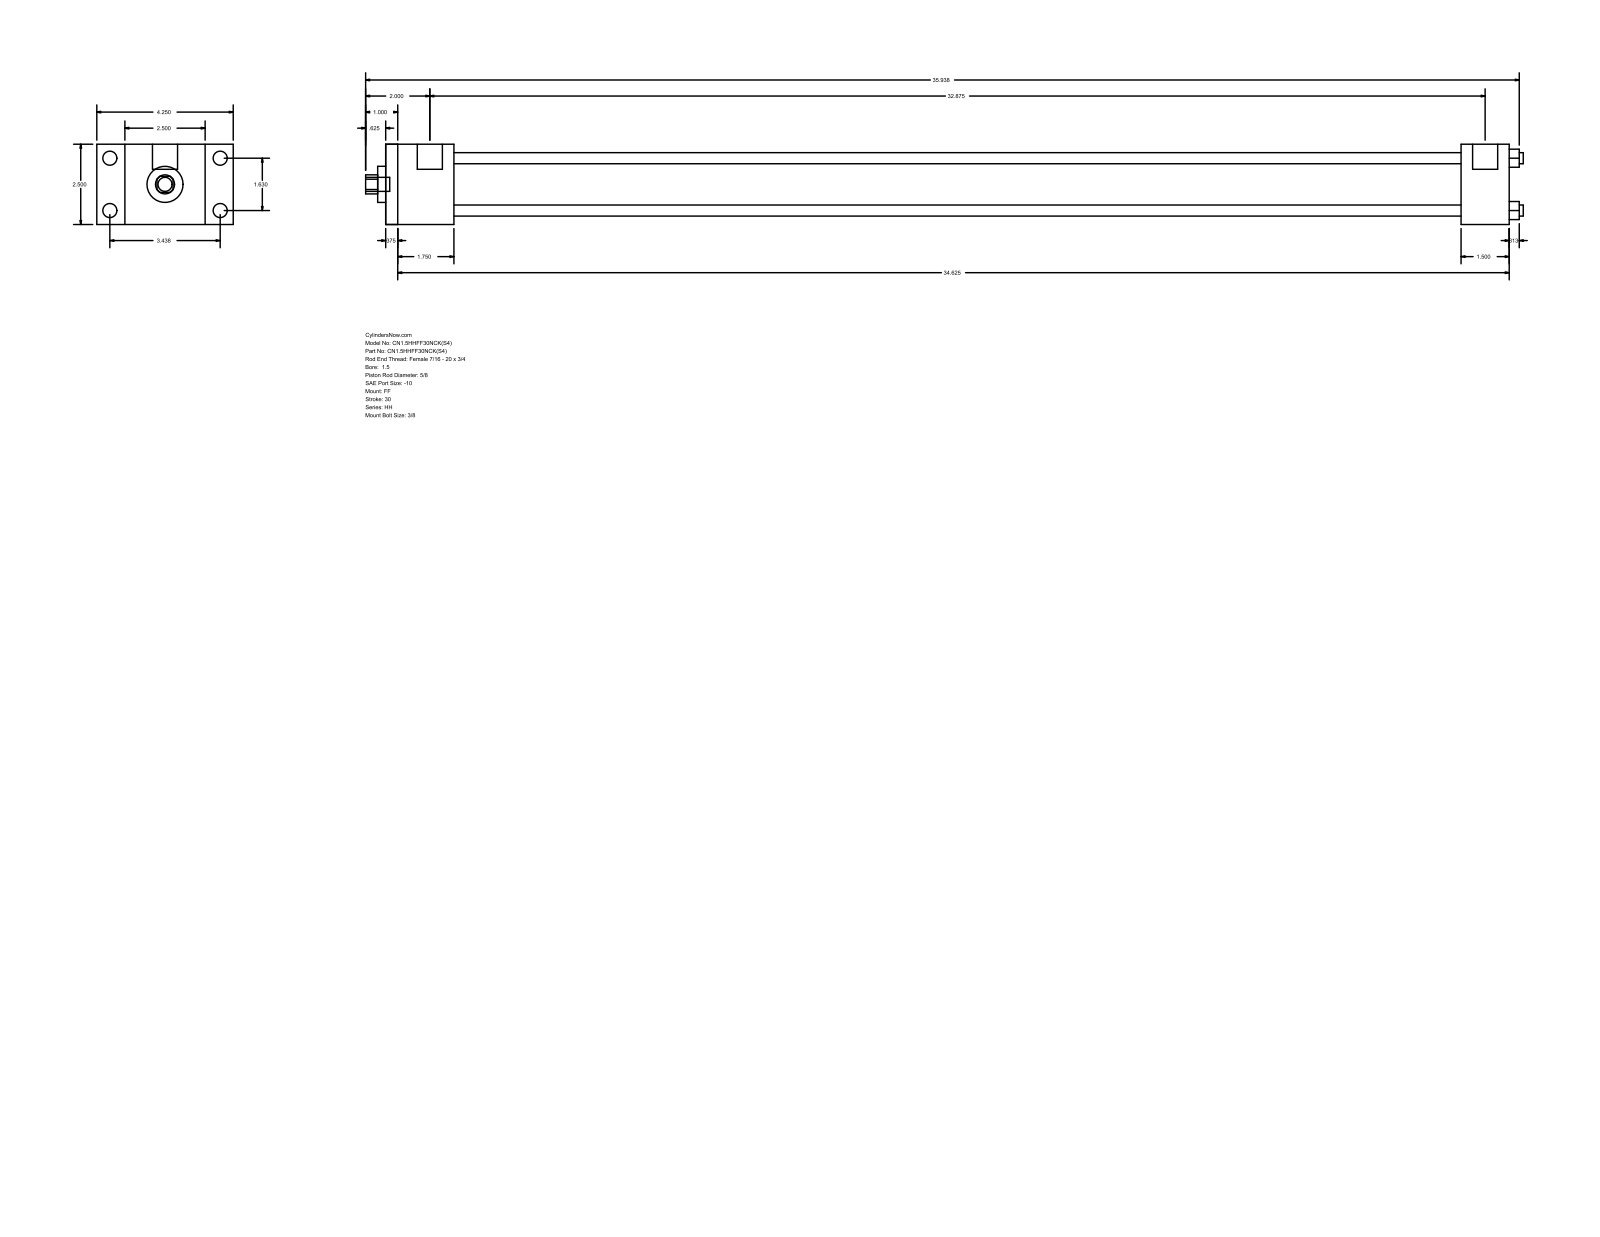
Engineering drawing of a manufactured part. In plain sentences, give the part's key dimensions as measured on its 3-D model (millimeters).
The part is named "HH_FF__0150_0.625". Its 3-D file was written by "GSSL Pune (CONFIG_CONTROL_DESIGN)". It is 0 solids with 92 faces: 64 planar, 28 cylindrical and 0 other. Overall it measures 915.99 by 107.95 by 63.5 millimeters. Round holes: 4 of diameter 8.76, 1 of diameter 15.88, 1 of diameter 28.57, 1 of diameter 44.45. Round bosses or shafts: 4 of diameter 11.13, 4 of diameter 5.56, 2 of diameter 19.84, 1 of diameter 11.11. Partial cylindrical surfaces (rounded edges, fillets, slot ends): 1 of radius 7.54. The main face-to-face distances are 63.5, 889, 9.52, 879.48, 53.97, 44.45, 835.03, 850.89, 841.37, 796.92. The hole center spacings are 29.27, 41.4, 58.55.
